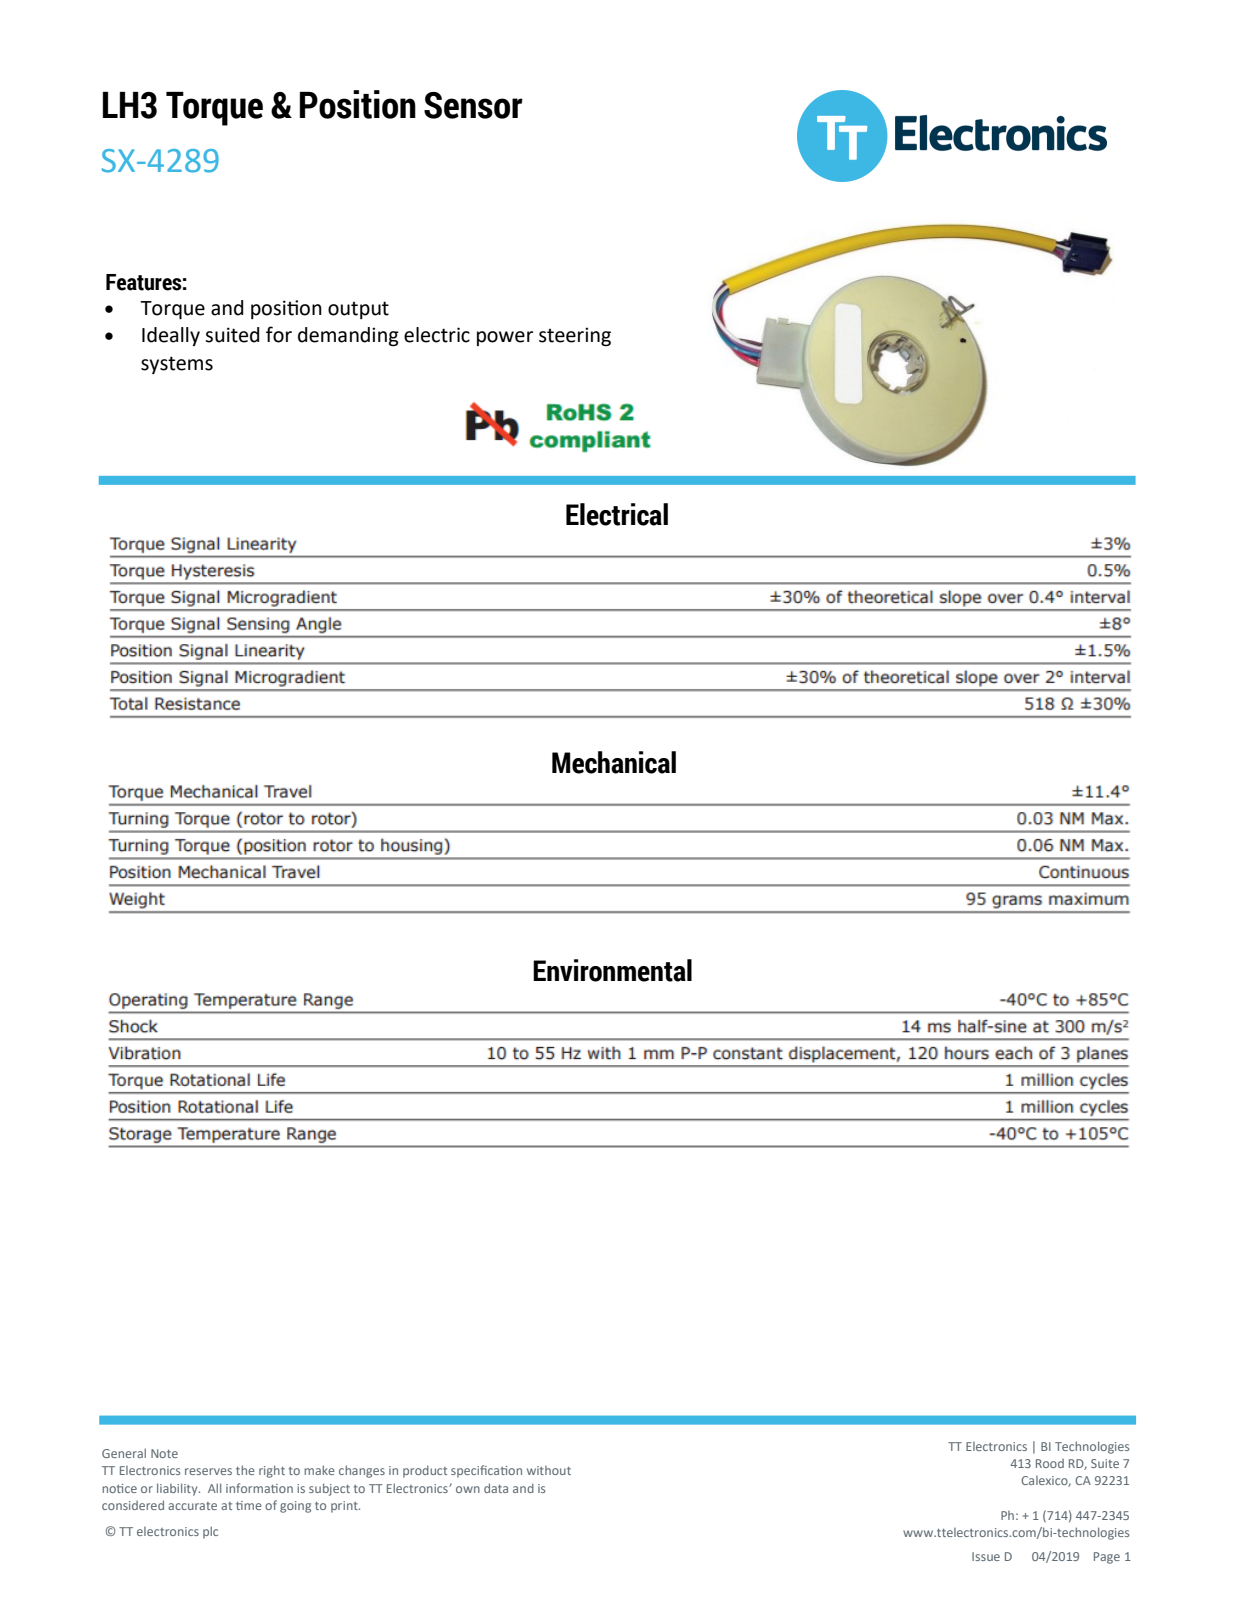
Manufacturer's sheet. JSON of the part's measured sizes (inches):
{"part_name": "SX-4289_SW0001", "step_written_by": "PRO/ENGINEER BY PARAMETRIC TECHNOLOGY CORPORATION, 2012230 (CONFIG_CONTROL_DESIGN)", "units": "inches", "bodies": {"solids": 4, "faces": 1573, "planar": 683, "cylindrical": 567, "other": 323}, "overall_size": [14.169, 5.134, 1.839], "volume_in3": 6.43, "surface_area_in2": 54.37, "round_holes": [[0.042, 7], [0.039, 5], [1.046, 1], [1.126, 1], [1.146, 1], [1.2, 1], [1.255, 1], [3.15, 1]], "round_bosses_or_shafts": [[0.04, 7], [0.047, 6], [0.35, 2], [3.2, 1], [3.142, 1], [3.1, 1], [3.056, 1], [1.345, 1]], "partial_cylinders_radius": [[0.007, 72], [0.012, 72], [0.005, 38], [0.01, 32], [0.02, 22], [0.016, 19], [0.006, 18], [0.028, 18]], "face_to_face_distances": [0.719, 0.521, 0.065, 0.047, 0.012, 0.114, 0.729, 0.12, 0.077, 0.796], "hole_center_spacings": [0.115, 0.23, 0.23, 0.345, 0.345, 0.46, 0.575, 0.115]}
